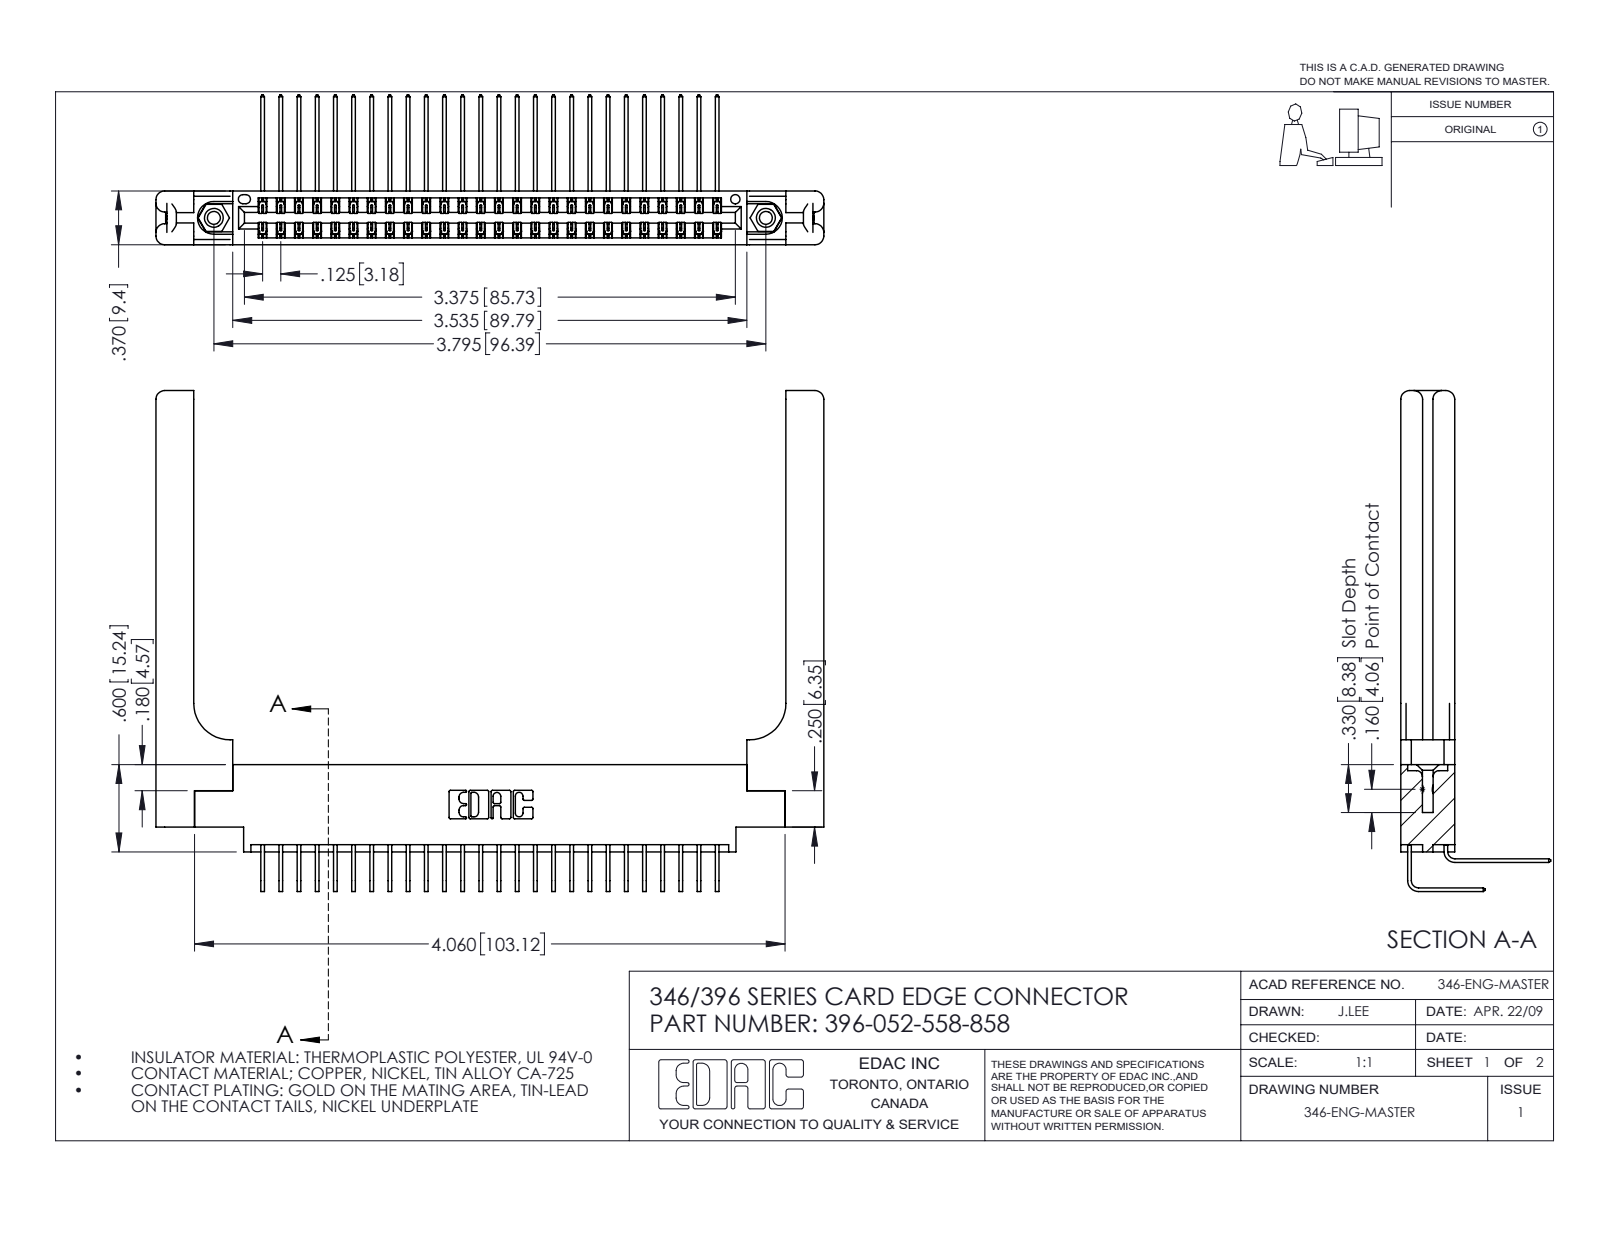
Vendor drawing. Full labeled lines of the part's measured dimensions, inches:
Part name (STEP PRODUCT): 346-220-058_345-220-058; 345-250-001_345-250-001-102; 396-052-558-858; 345-292-001_558 Tail - 2 (+2 more)
STEP written by: SolidWorks 2016 (CONFIG_CONTROL_DESIGN)
Units: inches
Bodies: 57 solids, 3190 faces (2152 planar, 978 cylindrical, 60 other)
Overall size (bounding box): 4.591 × 3.443 × 1.03
Volume: 1.153 in³ · Surface area: 34.1 in²
Round holes (diameter × count): ⌀0.089 ×2, ⌀0.125 ×2, ⌀0.156 ×2, ⌀0.064 ×1
Round bosses / shafts (diameter × count): ⌀0.155 ×2
Partial cylindrical surfaces — rounded edges, fillets, slot ends (radius × count): R0.006 ×78, R0.01 ×22, R0.06 ×16, R0.007 ×6, R0.031 ×6, R0.026 ×3, R0.014 ×2, R0.022 ×2
Main face-to-face distances: 0.37, 0.072, 0.322, 0.048, 0.025, 0.148, 0.15, 0.25, 0.298, 0.275
Hole centre spacings: 0.246, 3.587, 3.795
